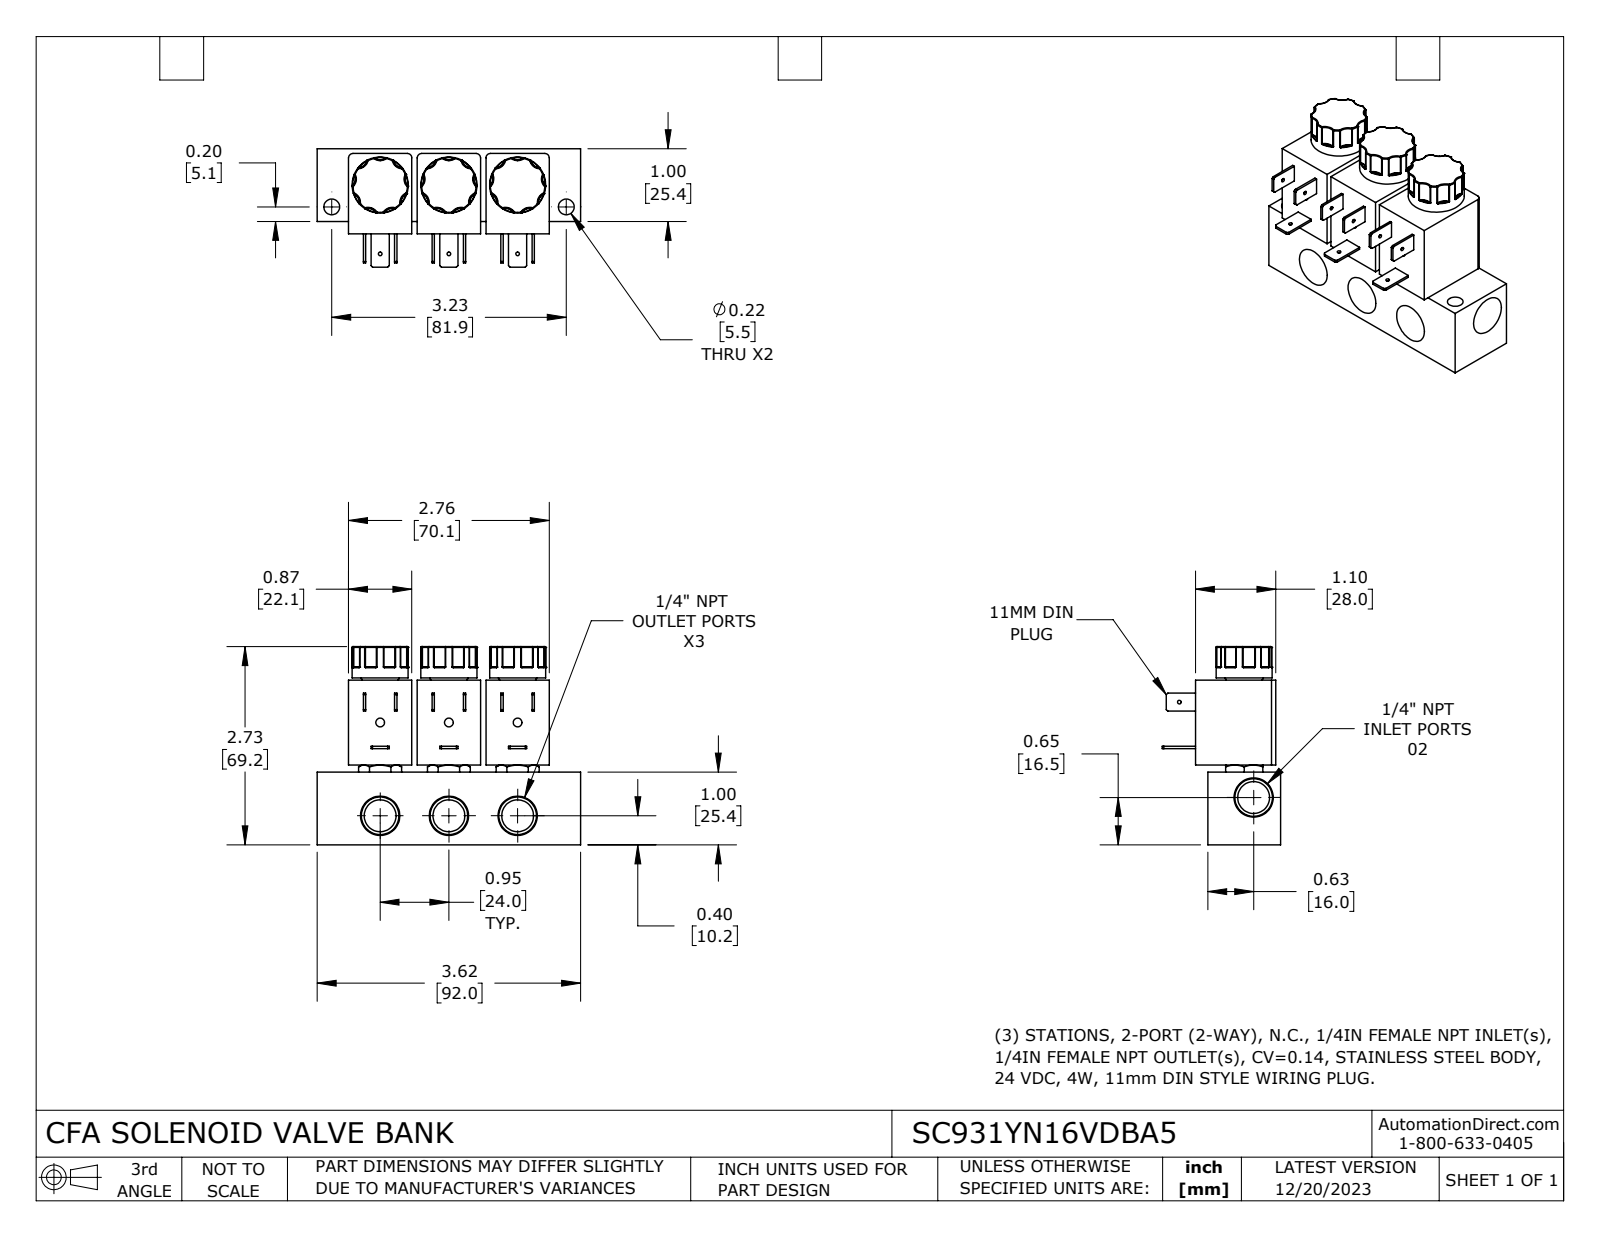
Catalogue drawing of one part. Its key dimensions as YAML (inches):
part_name: "SC931YN16VDBA5"
step_written_by: "SolidWorks 2023 (CONFIG_CONTROL_DESIGN)"
units: inches
bodies: {solids: 1, faces: 657, planar: 146, cylindrical: 140, other: 371}
overall_size: [3.622, 2.725, 1.627]
volume: 7.008
surface_area: 47.81
round_holes:
  - {diameter: 0.05, count: 4}
  - {diameter: 0.438, count: 4}
  - {diameter: 0.12, count: 3}
  - {diameter: 0.217, count: 2}
round_bosses_or_shafts:
  - {diameter: 0.77, count: 3}
partial_cylinders:
  - {radius: 0.01, count: 54}
  - {radius: 0.133, count: 25}
  - {radius: 0.06, count: 6}
  - {radius: 0.132, count: 2}
face_to_face_distances: [1, 0.945, 0.87, 1.169, 0.169, 0.065, 0.935, 1.104, 1.89, 1.815]
hole_center_spacings: [0.945, 1.593, 1.282, 1.89, 2.283, 0.928, 0.93, 1.662]
